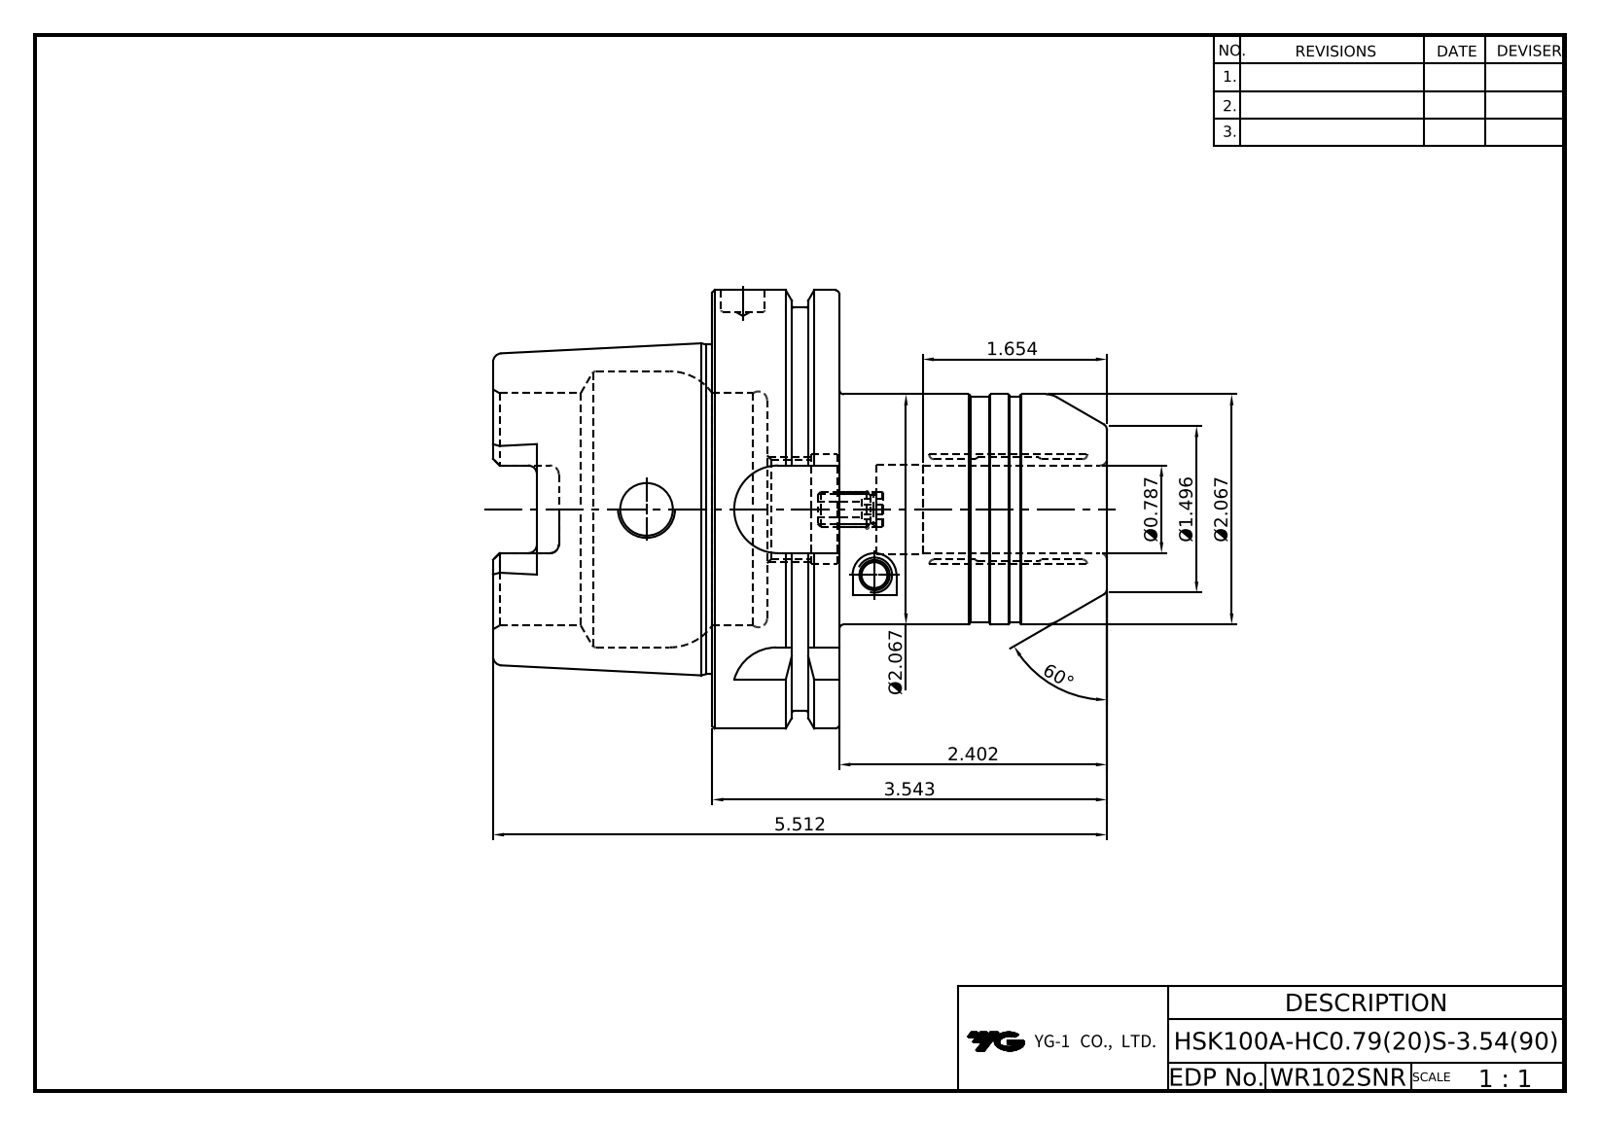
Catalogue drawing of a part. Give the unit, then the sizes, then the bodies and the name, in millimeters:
Units: millimetres
Overall size (bounding box): 140 × 100 × 100
Round holes (diameter × count): ⌀6.92 ×1, ⌀10 ×1, ⌀12 ×1, ⌀20 ×1, ⌀20.6 ×1, ⌀22.38 ×1, ⌀25 ×1, ⌀53 ×1, ⌀63 ×1
Round bosses / shafts (diameter × count): ⌀100 ×1, ⌀92 ×1, ⌀75.41 ×1, ⌀52.5 ×1, ⌀51.5 ×1
Partial cylindrical surfaces — rounded edges, fillets, slot ends (radius × count): R2 ×6, R4.88 ×4, R10 ×4
Main face-to-face distances: 29, 12.5, 16.5, 62.5, 50, 79, 77.5, 140, 90, 61
Volume: 361 969 mm³ · Surface area: 62 240 mm²
Bodies: 1 solid, 122 faces (38 planar, 38 cylindrical, 46 other)
Part name (STEP PRODUCT): HSK100A-HC20S-90
STEP written by: Autodesk Inventor 2022 (AUTOMOTIVE_DESIGN)
